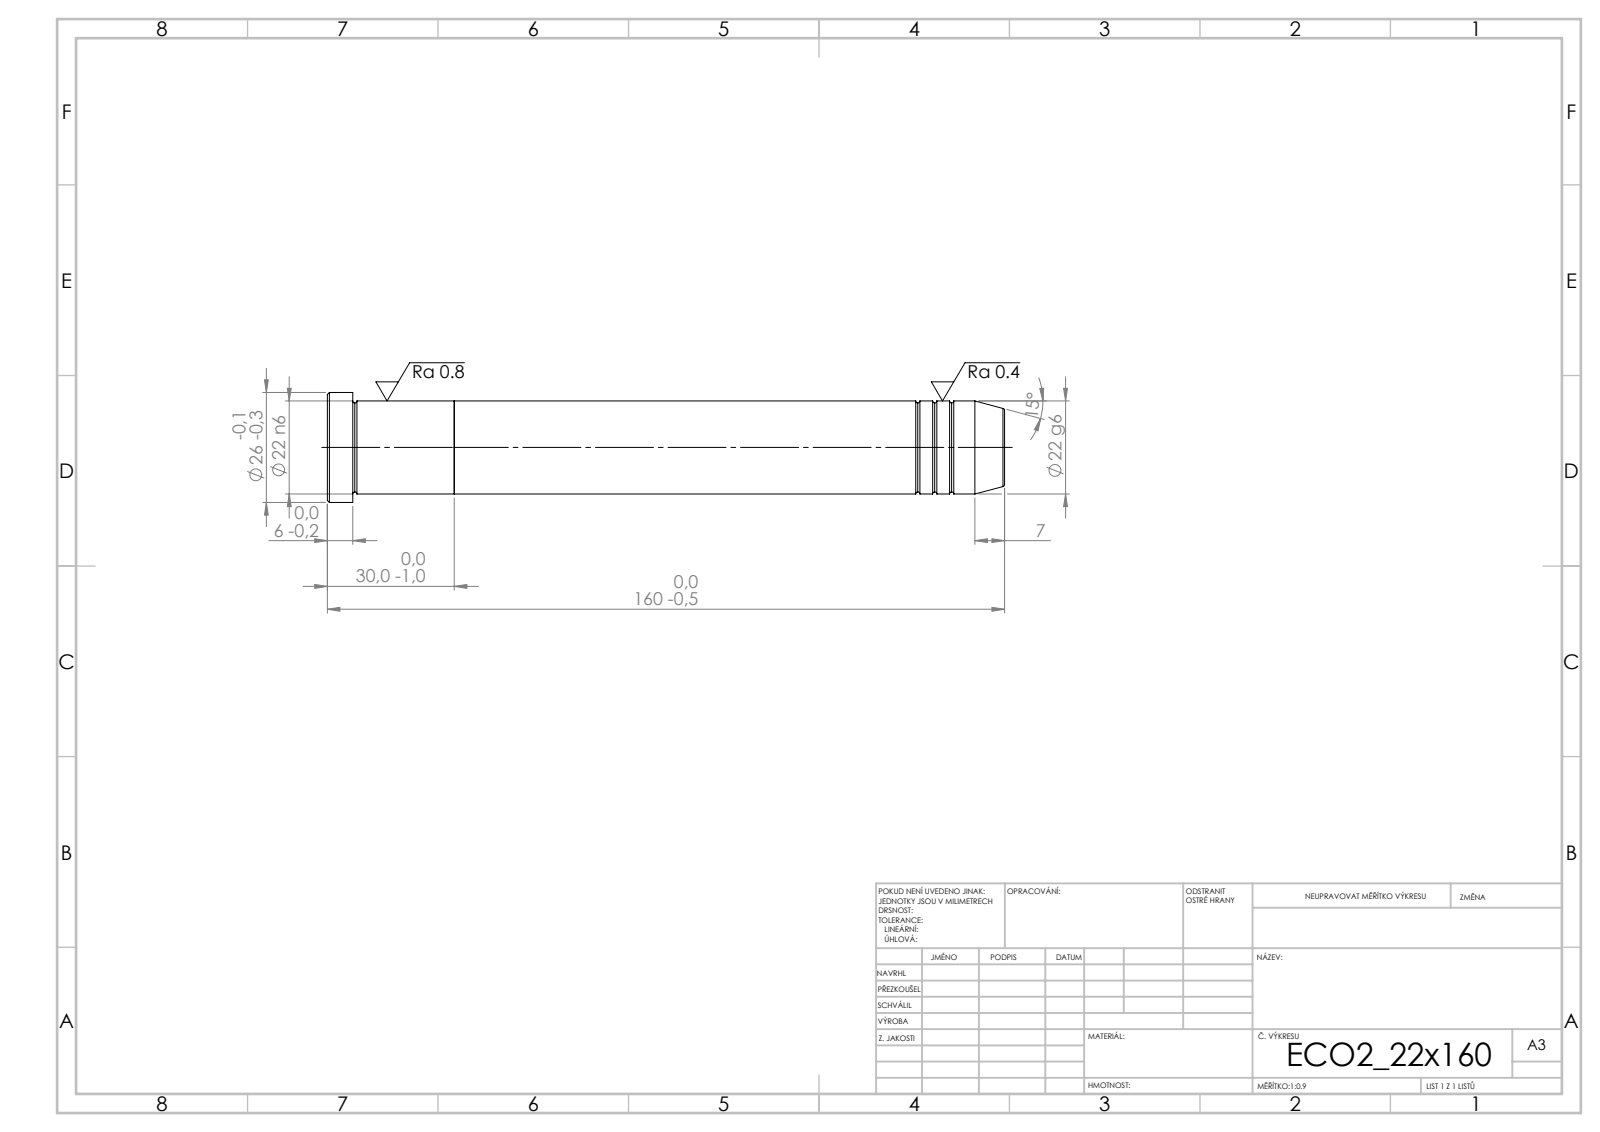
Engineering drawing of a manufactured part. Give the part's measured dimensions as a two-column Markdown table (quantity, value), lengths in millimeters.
| quantity | value |
| --- | --- |
| STEP written by | SolidWorks 2019 (CONFIG_CONTROL_DESIGN) |
| units | millimeters |
| bodies | 2 solids, 39 faces (5 planar, 12 cylindrical, 22 other) |
| overall size | 160 × 26 × 26 |
| volume | 61 180 mm³ |
| surface area | 12 926 mm² |
| round bosses / shafts (diameter × count) | 26 × 1, 22 × 1 |
| main face-to-face distances | 30, 130, 160, 154, 24, 6 |
